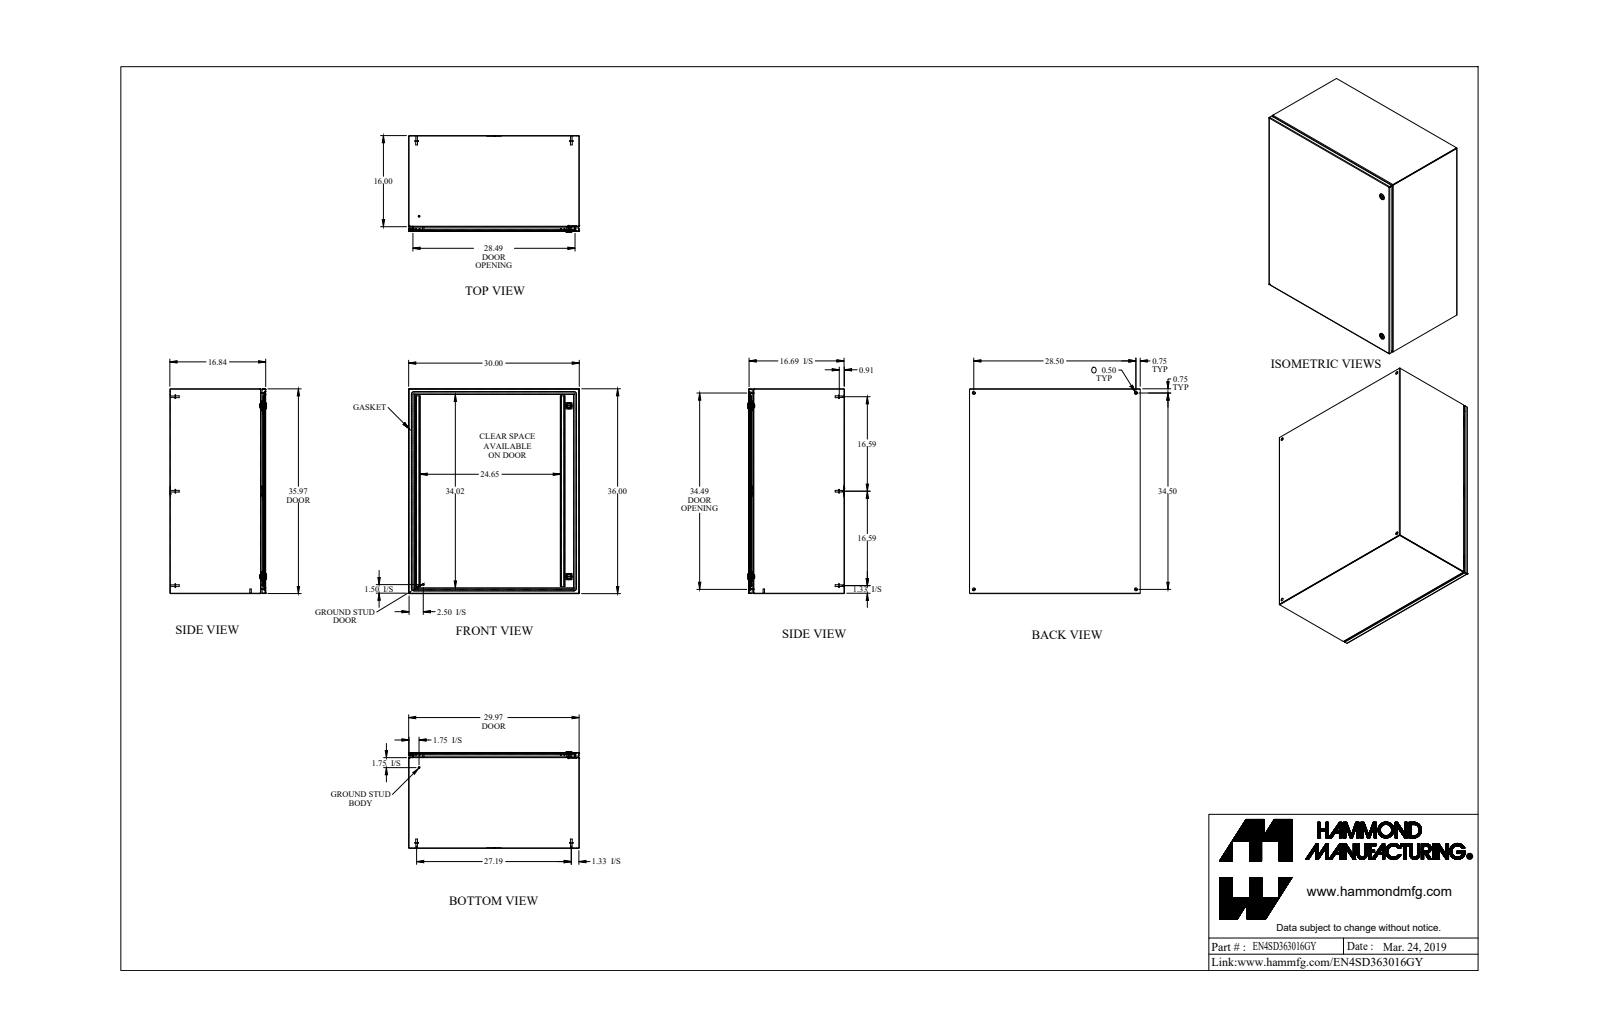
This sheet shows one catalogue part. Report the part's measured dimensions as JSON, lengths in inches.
{"part_name": "EN4SD363016GY", "step_written_by": "SolidWorks 2019 (AUTOMOTIVE_DESIGN)", "units": "inches", "bodies": {"solids": 35, "faces": 901, "planar": 434, "cylindrical": 295, "other": 172}, "overall_size": [36, 30, 16.997], "volume_in3": 343.1, "surface_area_in2": 9612, "round_holes": [[0.5, 4], [0.232, 2], [0.625, 2], [0.785, 2], [0.172, 1], [0.24, 1], [0.242, 1]], "round_bosses_or_shafts": [[0.625, 6], [0.313, 6], [0.27, 6], [1.1, 2], [0.525, 2], [0.281, 2], [0.25, 2], [0.455, 1]], "partial_cylinders_radius": [[0.036, 18], [0.108, 18], [0.043, 12], [0.081, 12], [0.312, 12], [0.006, 6], [0.062, 6], [0.125, 4]], "face_to_face_distances": [0.072, 16.765, 29.928, 16.693, 16.837, 35.928, 29.856, 30, 35.856, 36], "hole_center_spacings": [27.519, 28.5, 34.5, 44.749, 2.493, 2.494, 29.999, 32.267]}
